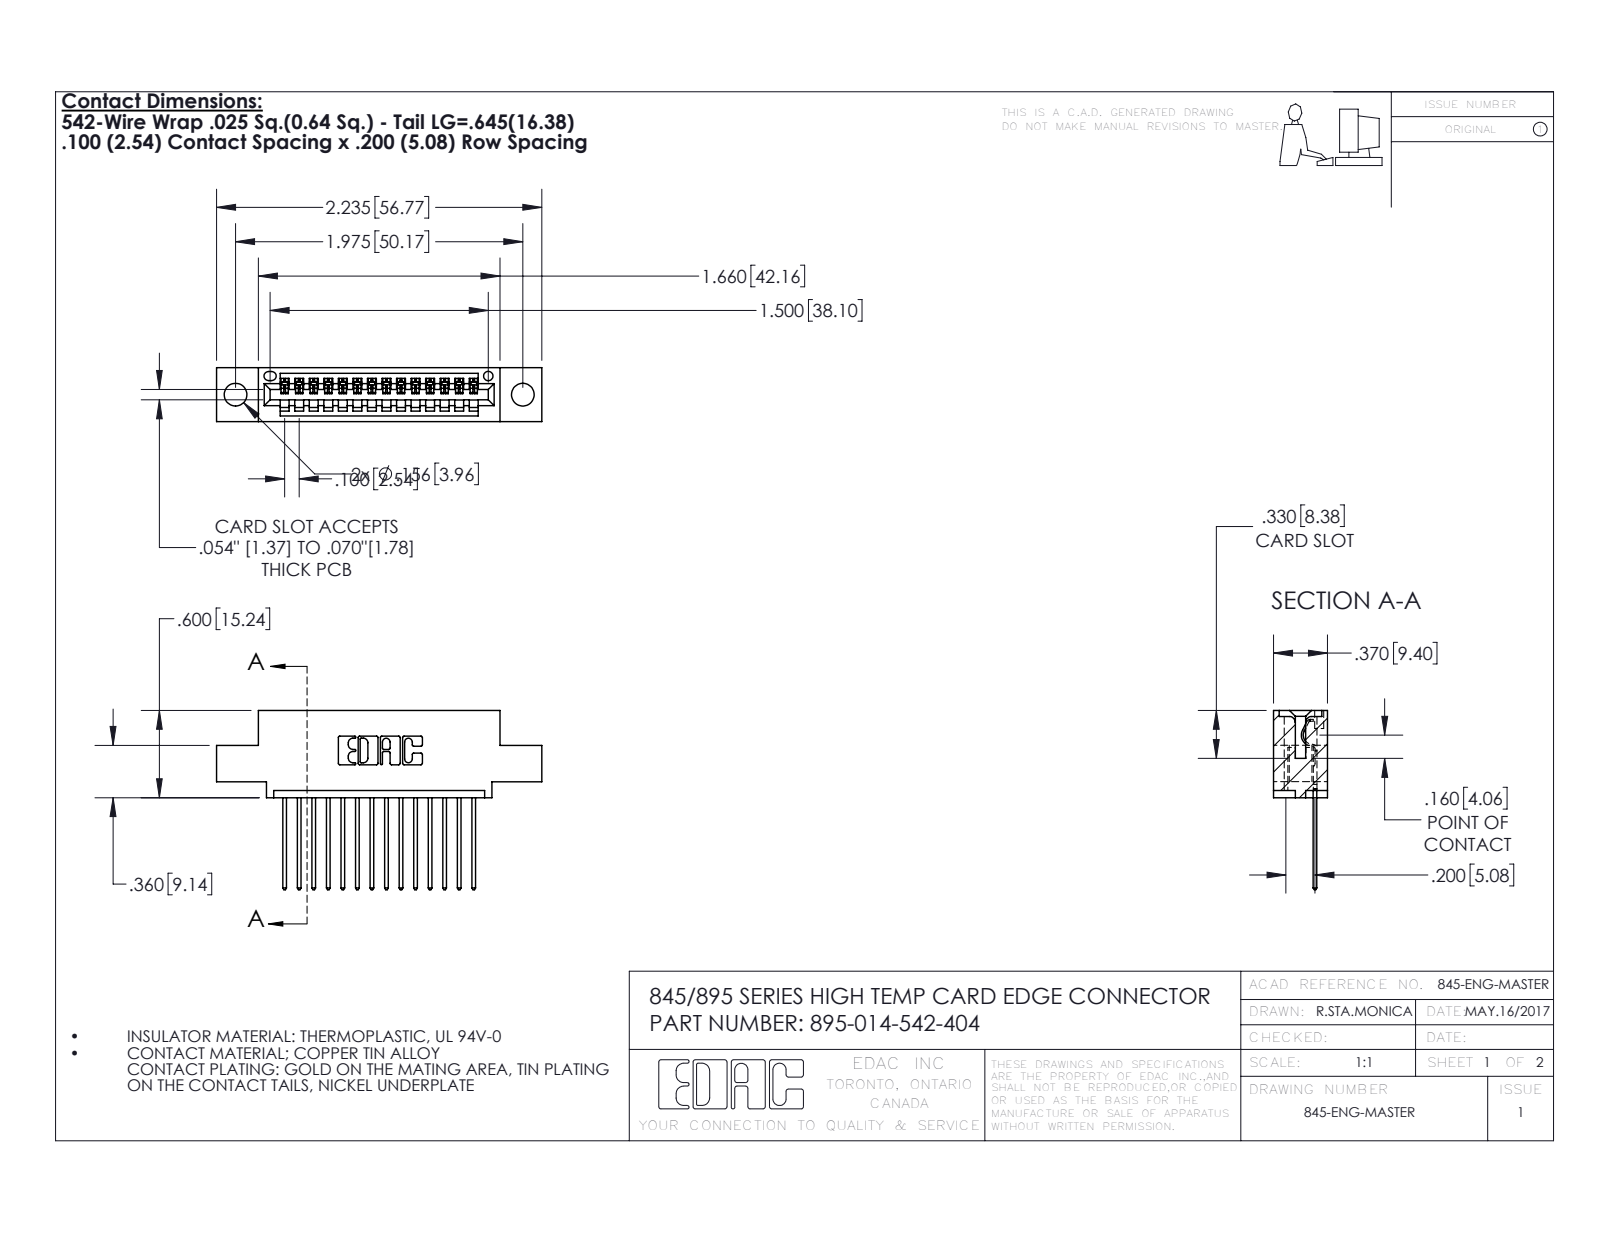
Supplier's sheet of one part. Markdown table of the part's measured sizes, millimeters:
| quantity | value |
| --- | --- |
| part name | 345 Part_0.110 Offset - 0.156 Dia-TH; 345-292-001_345-293-142; 395-014-542-404 |
| STEP written by | SolidWorks 2016 (CONFIG_CONTROL_DESIGN) |
| units | millimeters |
| bodies | 15 solids, 942 faces (644 planar, 298 cylindrical, 0 other) |
| overall size | 56.8 × 31.3 × 9.4 |
| volume | 5 030 mm³ |
| surface area | 6 395 mm² |
| round holes (diameter × count) | 4 × 2, 1.6 × 1 |
| partial cylindrical surfaces (radius × count) | 0.2 × 28, 0.3 × 28, 0.3 × 22, 0.2 × 6, 0.8 × 6, 0.7 × 3, 0.8 × 2, 1 × 2 |
| main face-to-face distances | 7.6, 1.8, 5.1, 9.4, 2.5, 6.9, 0.6, 5.7, 2.5, 7.6 |
| hole center spacings | 6.9, 44.2, 50.2 |
